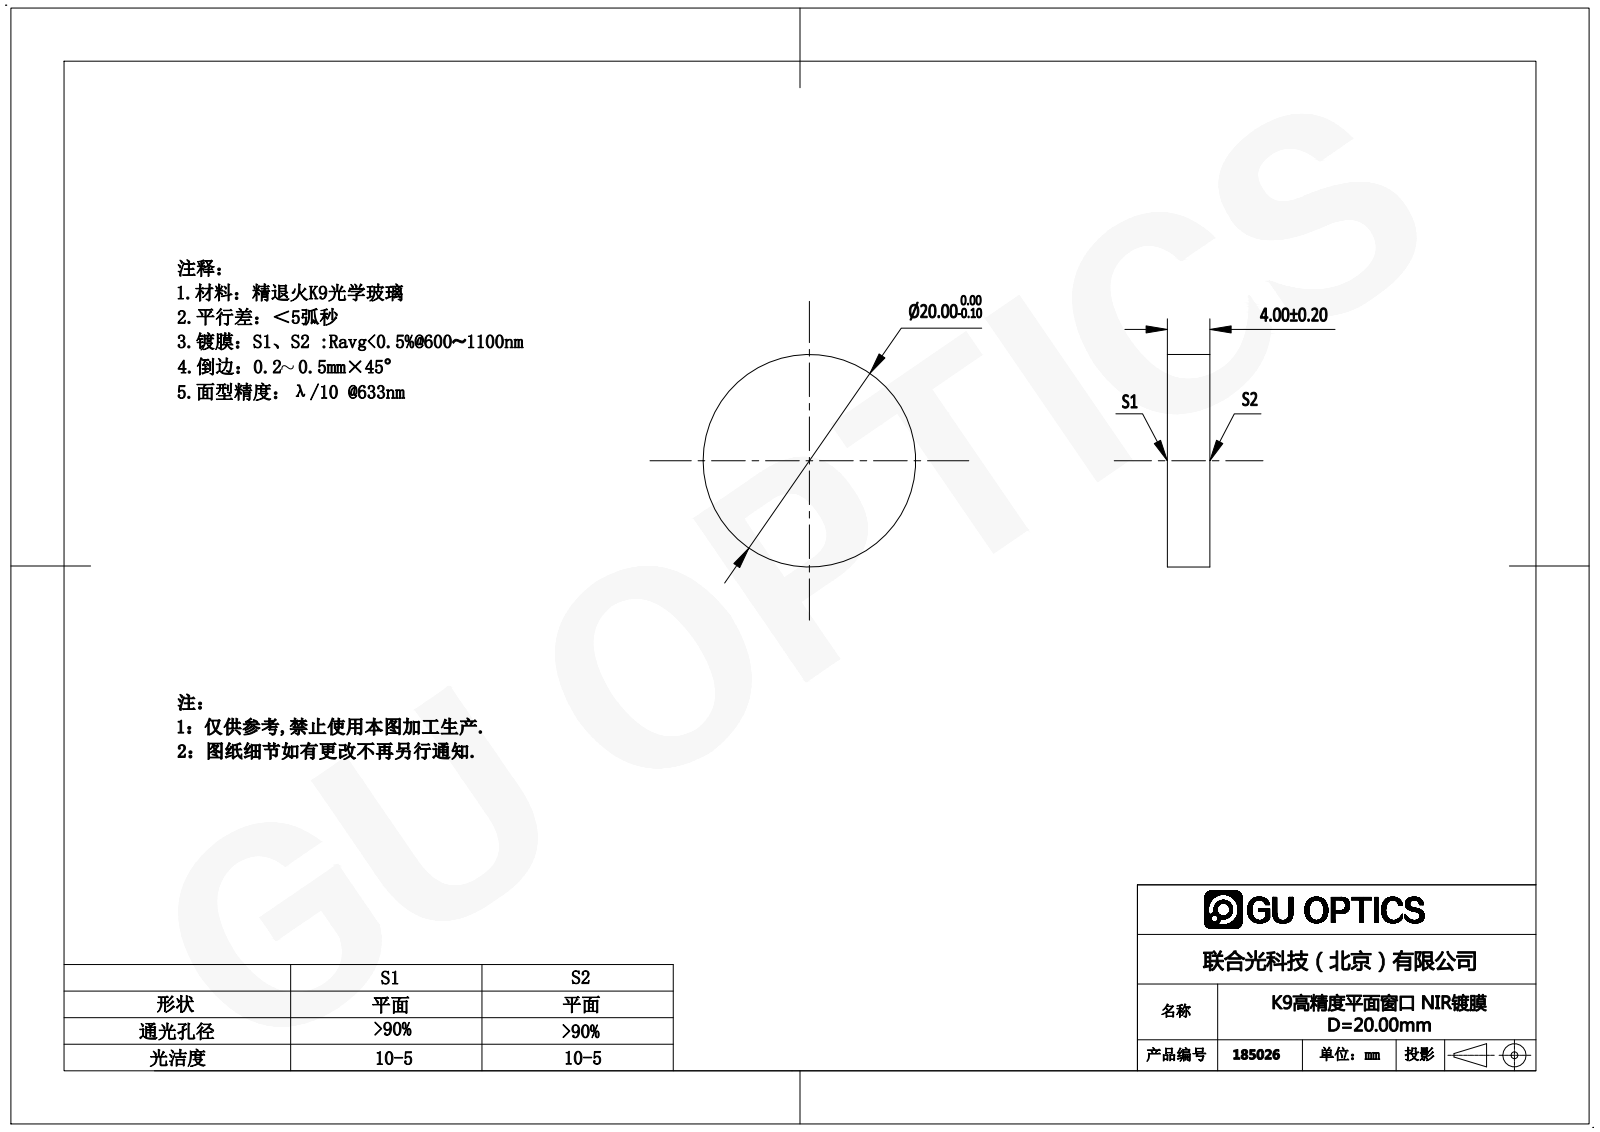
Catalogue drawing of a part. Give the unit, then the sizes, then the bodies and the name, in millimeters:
Units: millimetres
Overall size (bounding box): 20 × 20 × 4
Round bosses / shafts (diameter × count): ⌀20 ×1
Main face-to-face distances: 4
Volume: 1 257 mm³ · Surface area: 880 mm²
Bodies: 1 solid, 4 faces (2 planar, 2 cylindrical, 0 other)
Part name (STEP PRODUCT): 185004
STEP written by: SolidWorks 2016 (AUTOMOTIVE_DESIGN)
